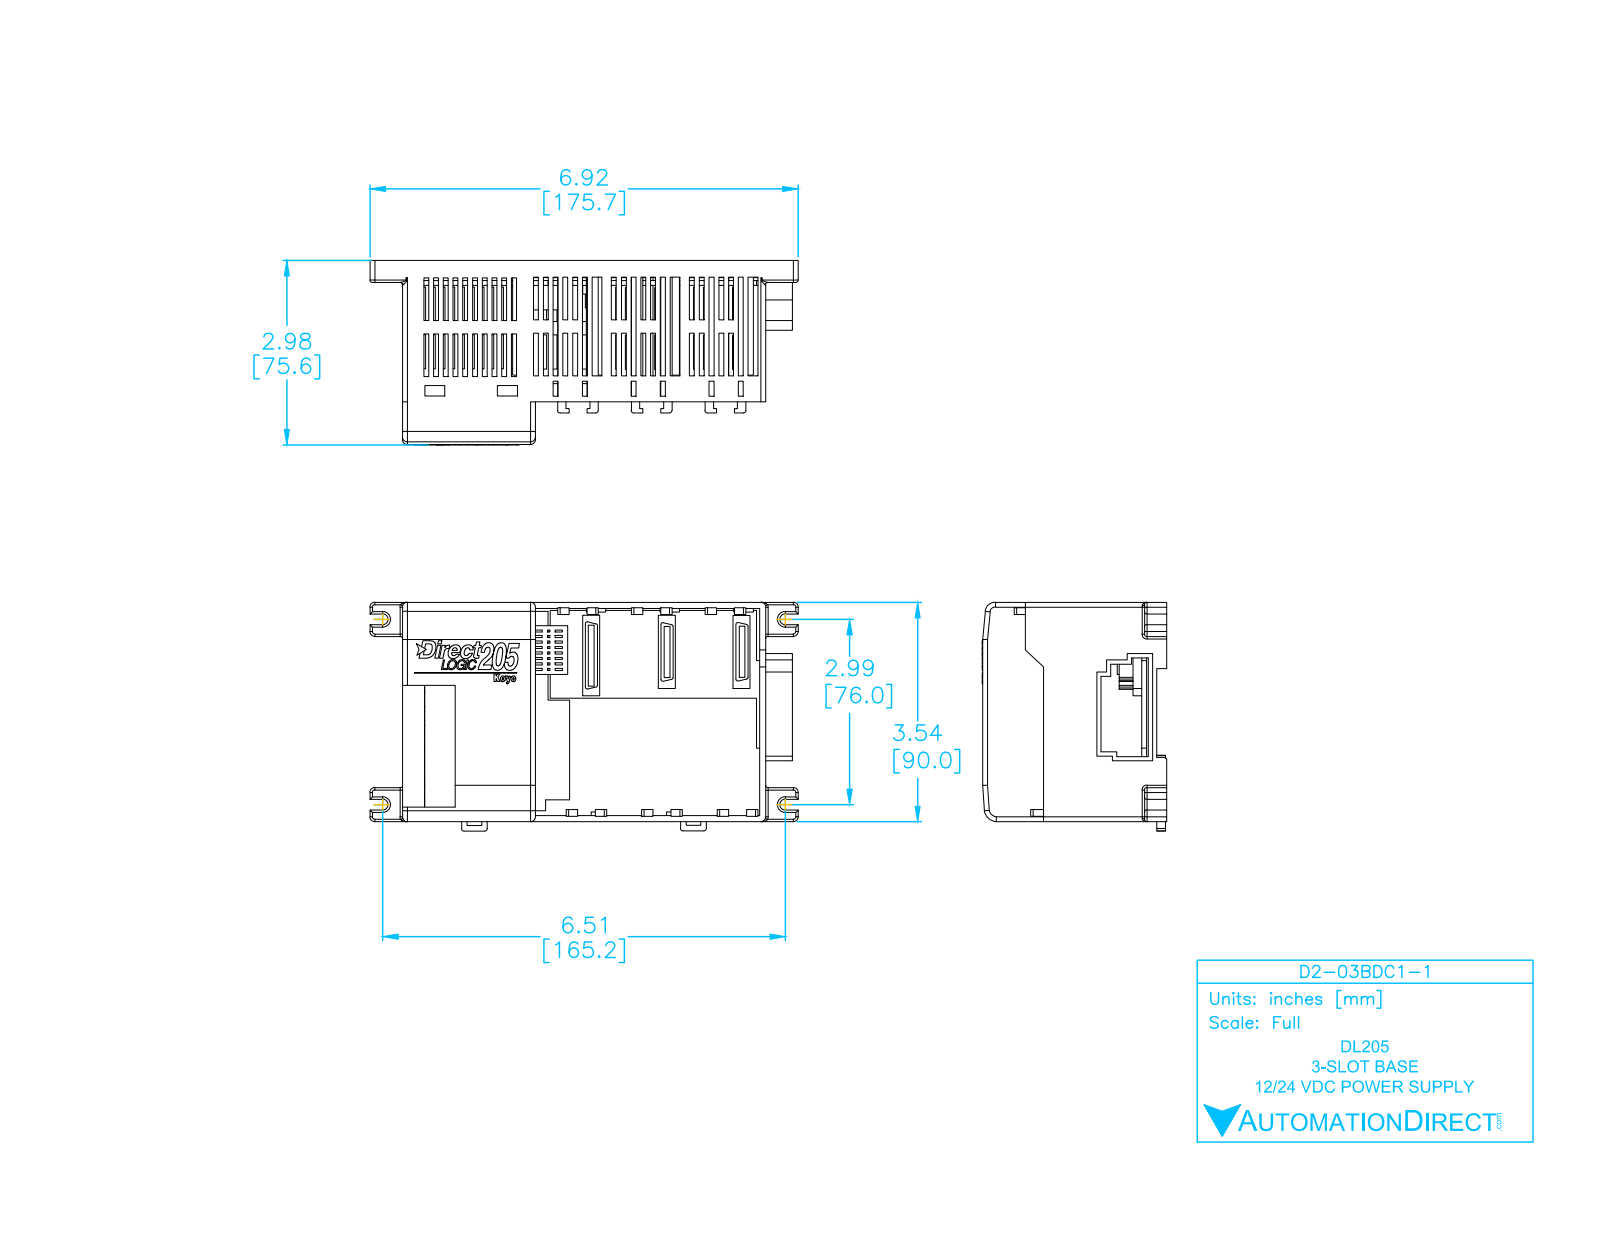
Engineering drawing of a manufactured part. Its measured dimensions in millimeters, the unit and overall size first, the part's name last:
Units: millimetres
Overall size (bounding box): 175.67 × 93.83 × 75.7
Round bosses / shafts (diameter × count): ⌀5.42 ×6
Partial cylindrical surfaces — rounded edges, fillets, slot ends (radius × count): R1 ×52, R2 ×20, R0.25 ×16, R0.75 ×12, R2.21 ×4, R4.71 ×4, R4.12 ×1, R5.29 ×1
Main face-to-face distances: 2.5, 3, 2, 1.25, 6.25, 4.25, 3.25, 87.5, 90, 146.5
Volume: 227 012 mm³ · Surface area: 137 768 mm²
Bodies: 5 solids, 1737 faces (1428 planar, 153 cylindrical, 156 other)
Part name (STEP PRODUCT): D2-03BDC1-1
STEP written by: SolidWorks 2009 (AUTOMOTIVE_DESIGN)
